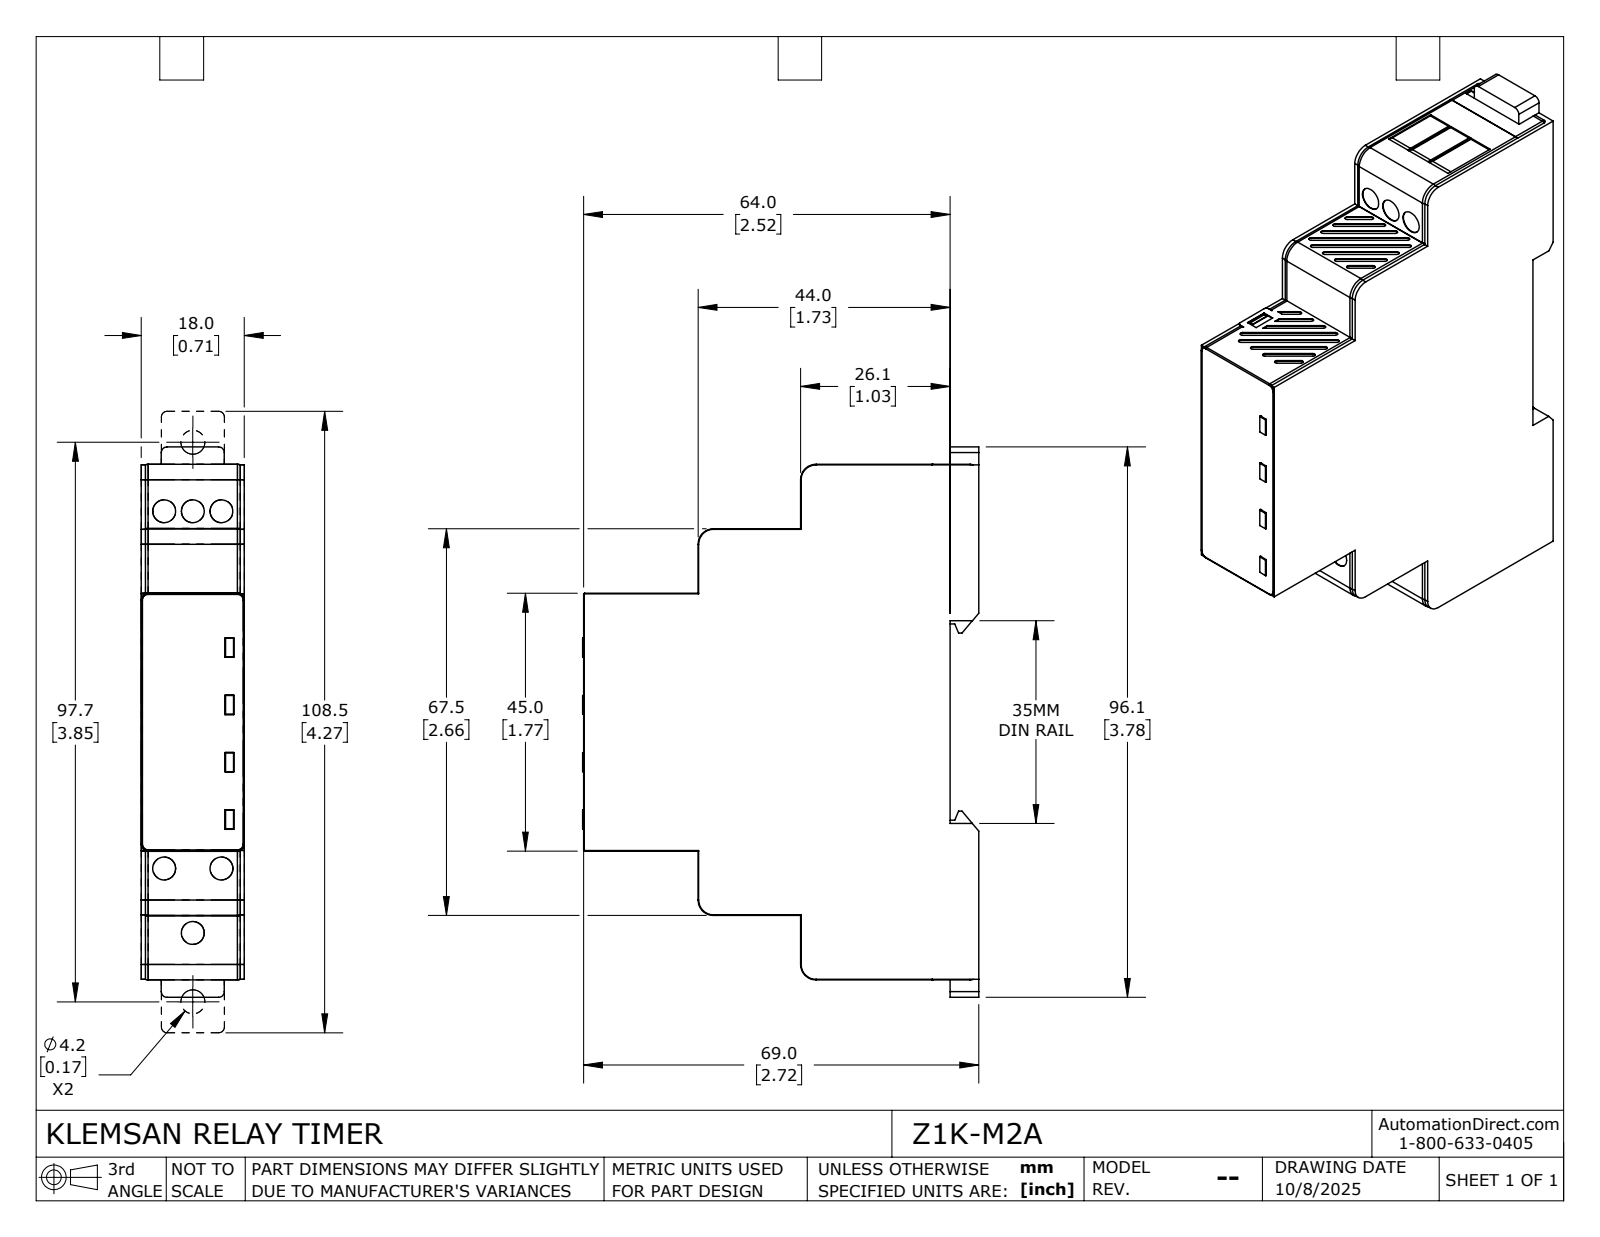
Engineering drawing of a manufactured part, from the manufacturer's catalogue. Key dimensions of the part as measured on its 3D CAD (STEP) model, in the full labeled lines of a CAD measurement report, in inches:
Part name (STEP PRODUCT): Z1K-M2A
STEP written by: SolidWorks 2024 (CONFIG_CONTROL_DESIGN)
Units: inches
Bodies: 3 solids, 440 faces (280 planar, 60 cylindrical, 100 other)
Overall size (bounding box): 3.782 × 2.722 × 0.709
Volume: 5.117 in³ · Surface area: 27.72 in²
Round holes (diameter × count): ⌀0.165 ×2, ⌀0.157 ×1
Partial cylindrical surfaces — rounded edges, fillets, slot ends (radius × count): R0.047 ×16, R0.008 ×4, R0.039 ×4, R0.102 ×4, R0.106 ×4, R0.02 ×2, R0.059 ×2
Main face-to-face distances: 0.709, 0.138, 0.571, 0.443, 2.52, 0.197, 2.717, 0.886, 2.654, 2.657
Hole centre spacings: 0.23, 3.127, 3.357
